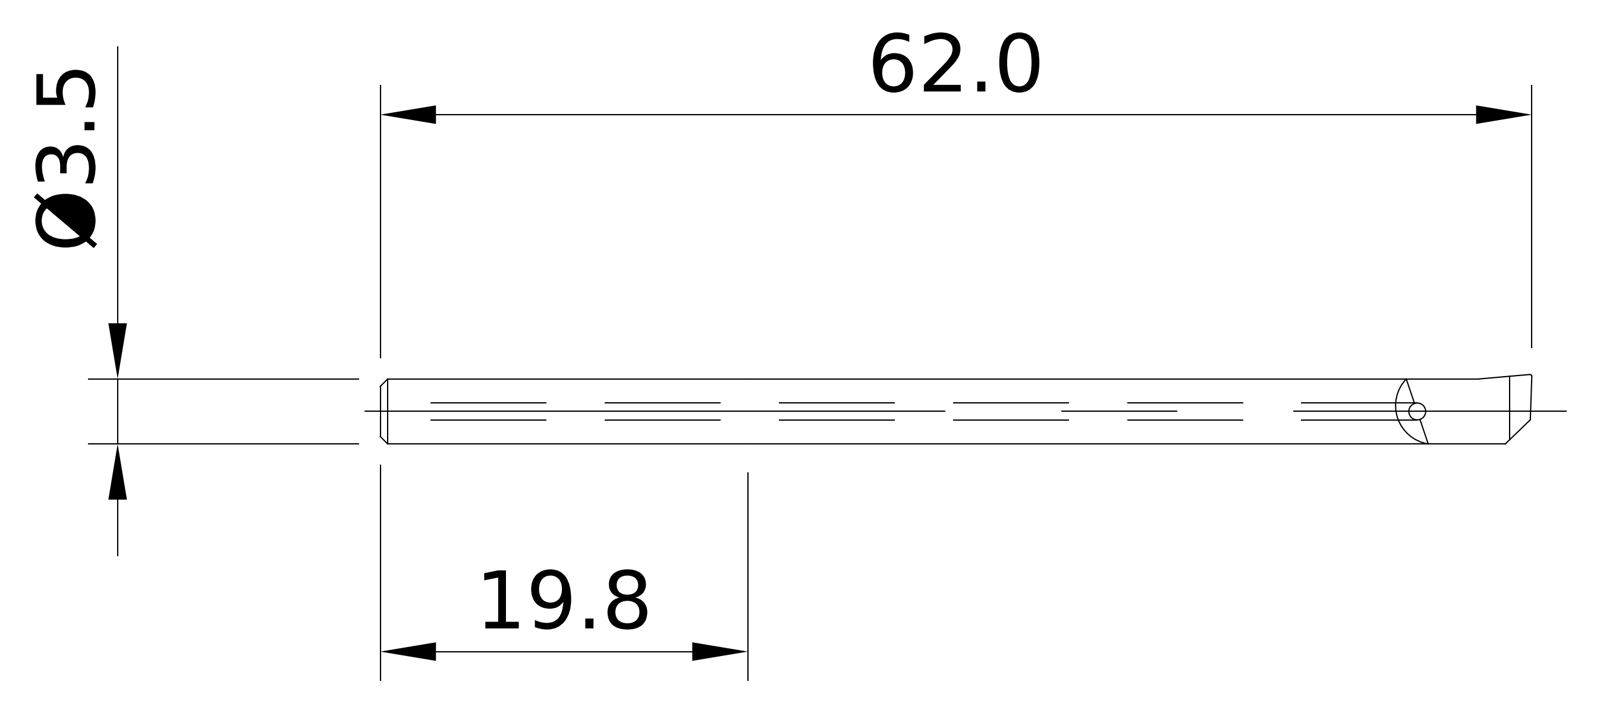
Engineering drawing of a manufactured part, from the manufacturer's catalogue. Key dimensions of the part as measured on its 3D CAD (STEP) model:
STEP written by: ACIS (automotive_design)
Units: millimetres
Bodies: 1 solid, 19 faces (10 planar, 5 cylindrical, 4 other)
Overall size (bounding box): 62 × 3.69 × 3.5
Volume: 536 mm³ · Surface area: 875 mm²
Round holes (diameter × count): ⌀1 ×1
Round bosses / shafts (diameter × count): ⌀3.5 ×1
Partial cylindrical surfaces — rounded edges, fillets, slot ends (radius × count): R0.25 ×1
